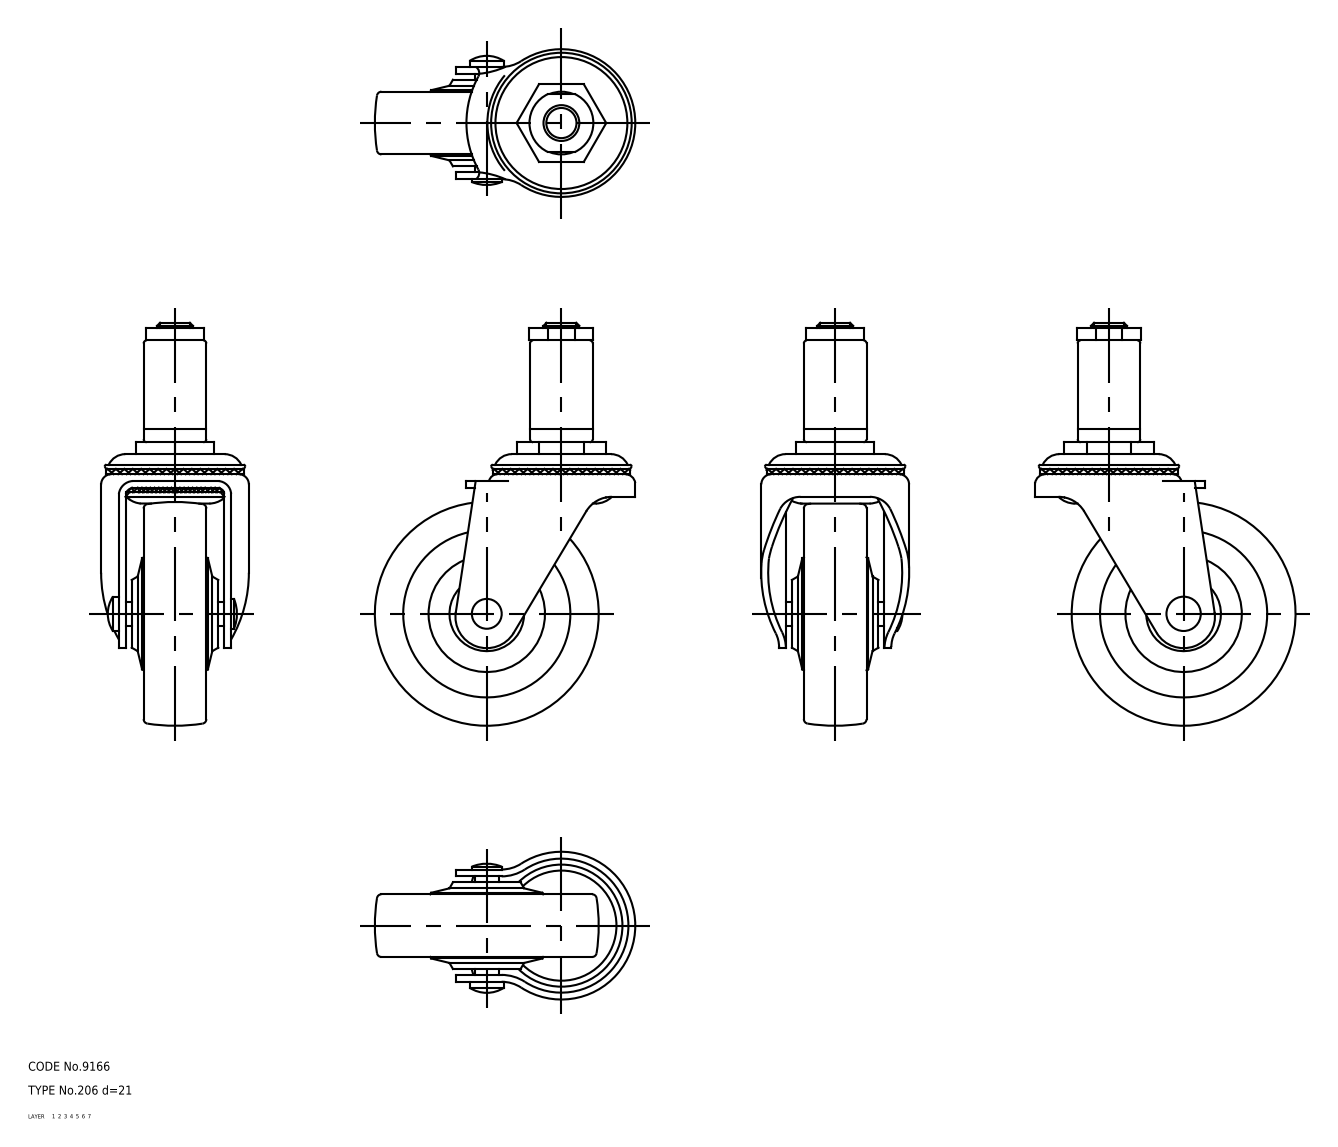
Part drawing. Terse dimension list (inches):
name: wheel; main shaft; axle; No_206_d21_6069_36
written by: CADfix (AUTOMOTIVE_DESIGN)
unit: in
bodies: 4 solids, 172 faces (0 planar, 0 cylindrical, 172 other)
size: 5.315 × 3.435 × 1.949
volume: 8.646 in³; area: 53.43 in²
